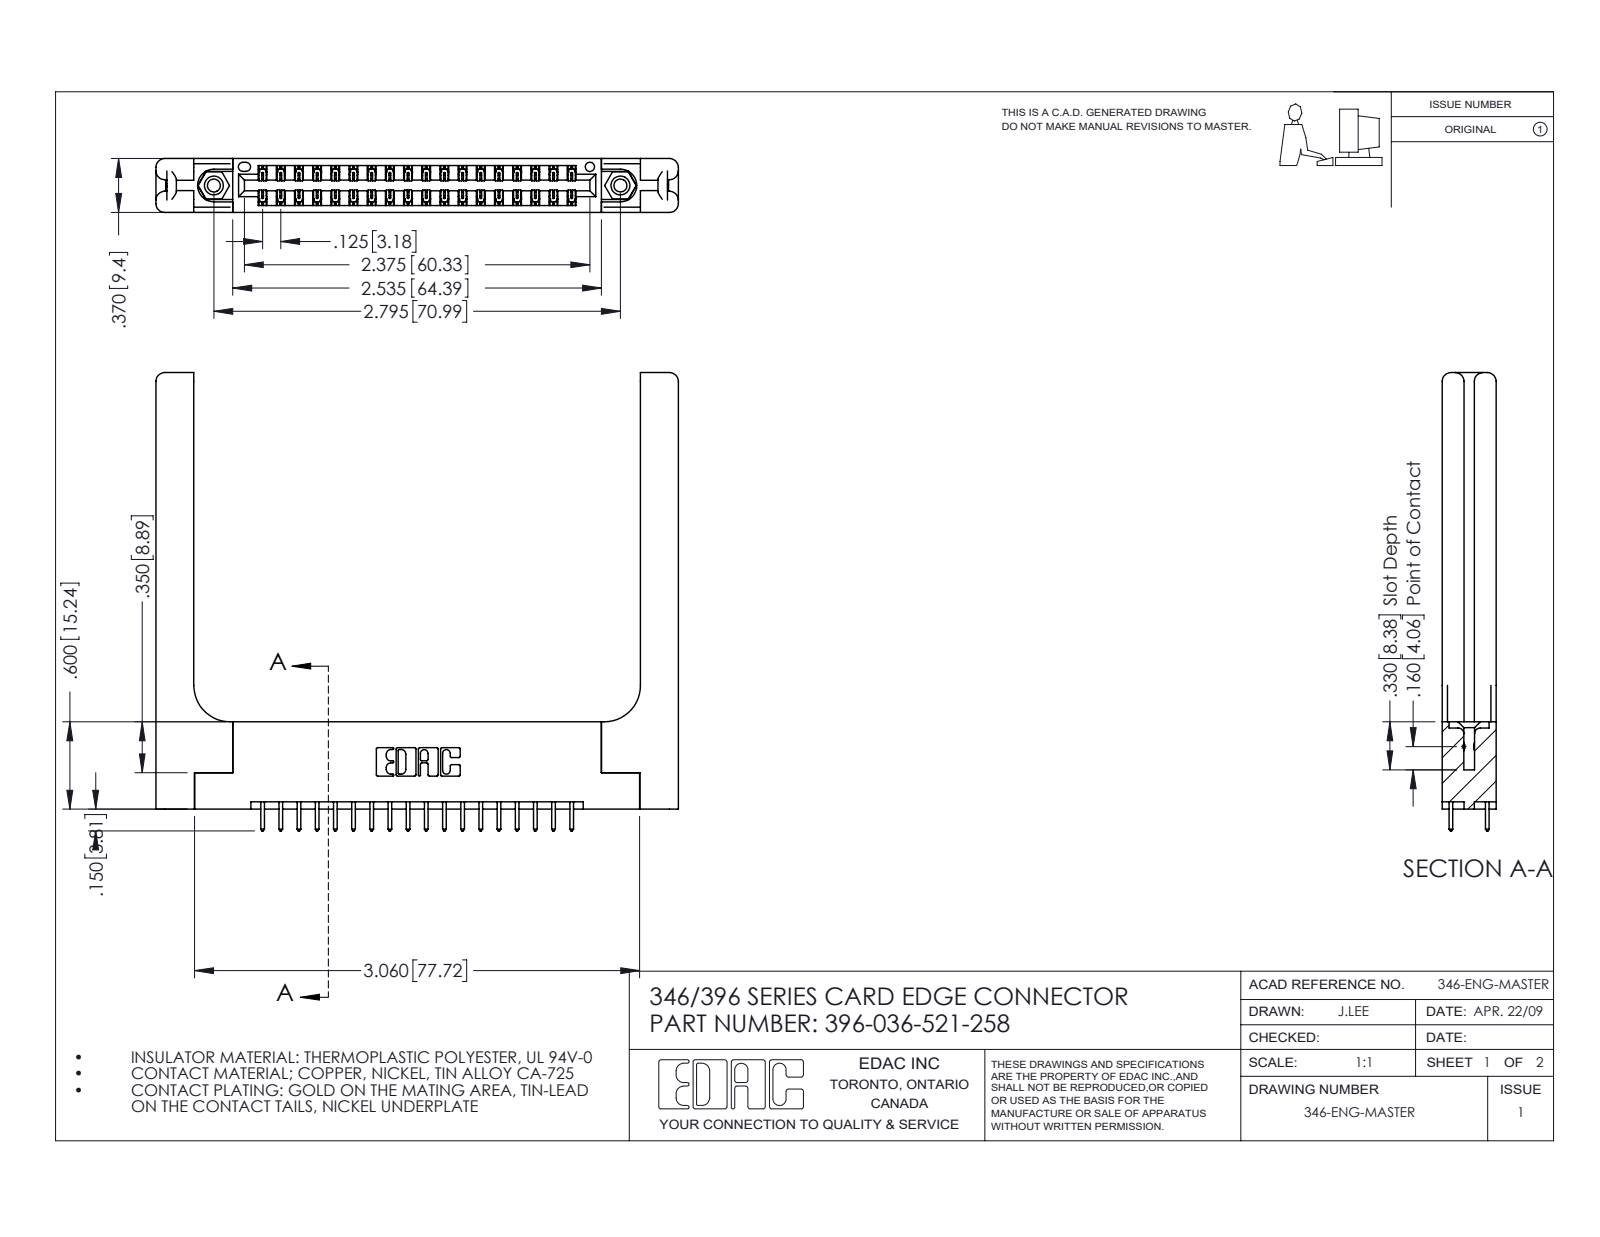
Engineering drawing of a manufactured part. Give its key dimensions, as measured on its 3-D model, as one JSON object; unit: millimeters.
{"part_name": "345-250-001_345-250-001-102; 346 Part_Flush Mounting Lugs - 0.156 Dia-TH; 396-036-521-258; 345-292-001_345-293-121 (+1 more)", "step_written_by": "SolidWorks 2016 (CONFIG_CONTROL_DESIGN)", "units": "millimeters", "bodies": {"solids": 41, "faces": 2250, "planar": 1484, "cylindrical": 706, "other": 60}, "overall_size": [91.2, 80, 9.4], "volume_mm3": 16200, "surface_area_mm2": 16450, "round_holes": [[2.3, 2], [3.2, 2], [4, 2], [1.6, 1]], "round_bosses_or_shafts": [[3.9, 2]], "partial_cylinders_radius": [[0.2, 54], [0.3, 36], [0.3, 22], [1.5, 16], [0.2, 6], [0.8, 6], [0.7, 3], [0.4, 2]], "face_to_face_distances": [9.4, 1.8, 3.8, 3.8, 1.2, 8.2, 6.4, 0.6, 2, 7.6], "hole_center_spacings": [6.2, 65.7, 71]}
